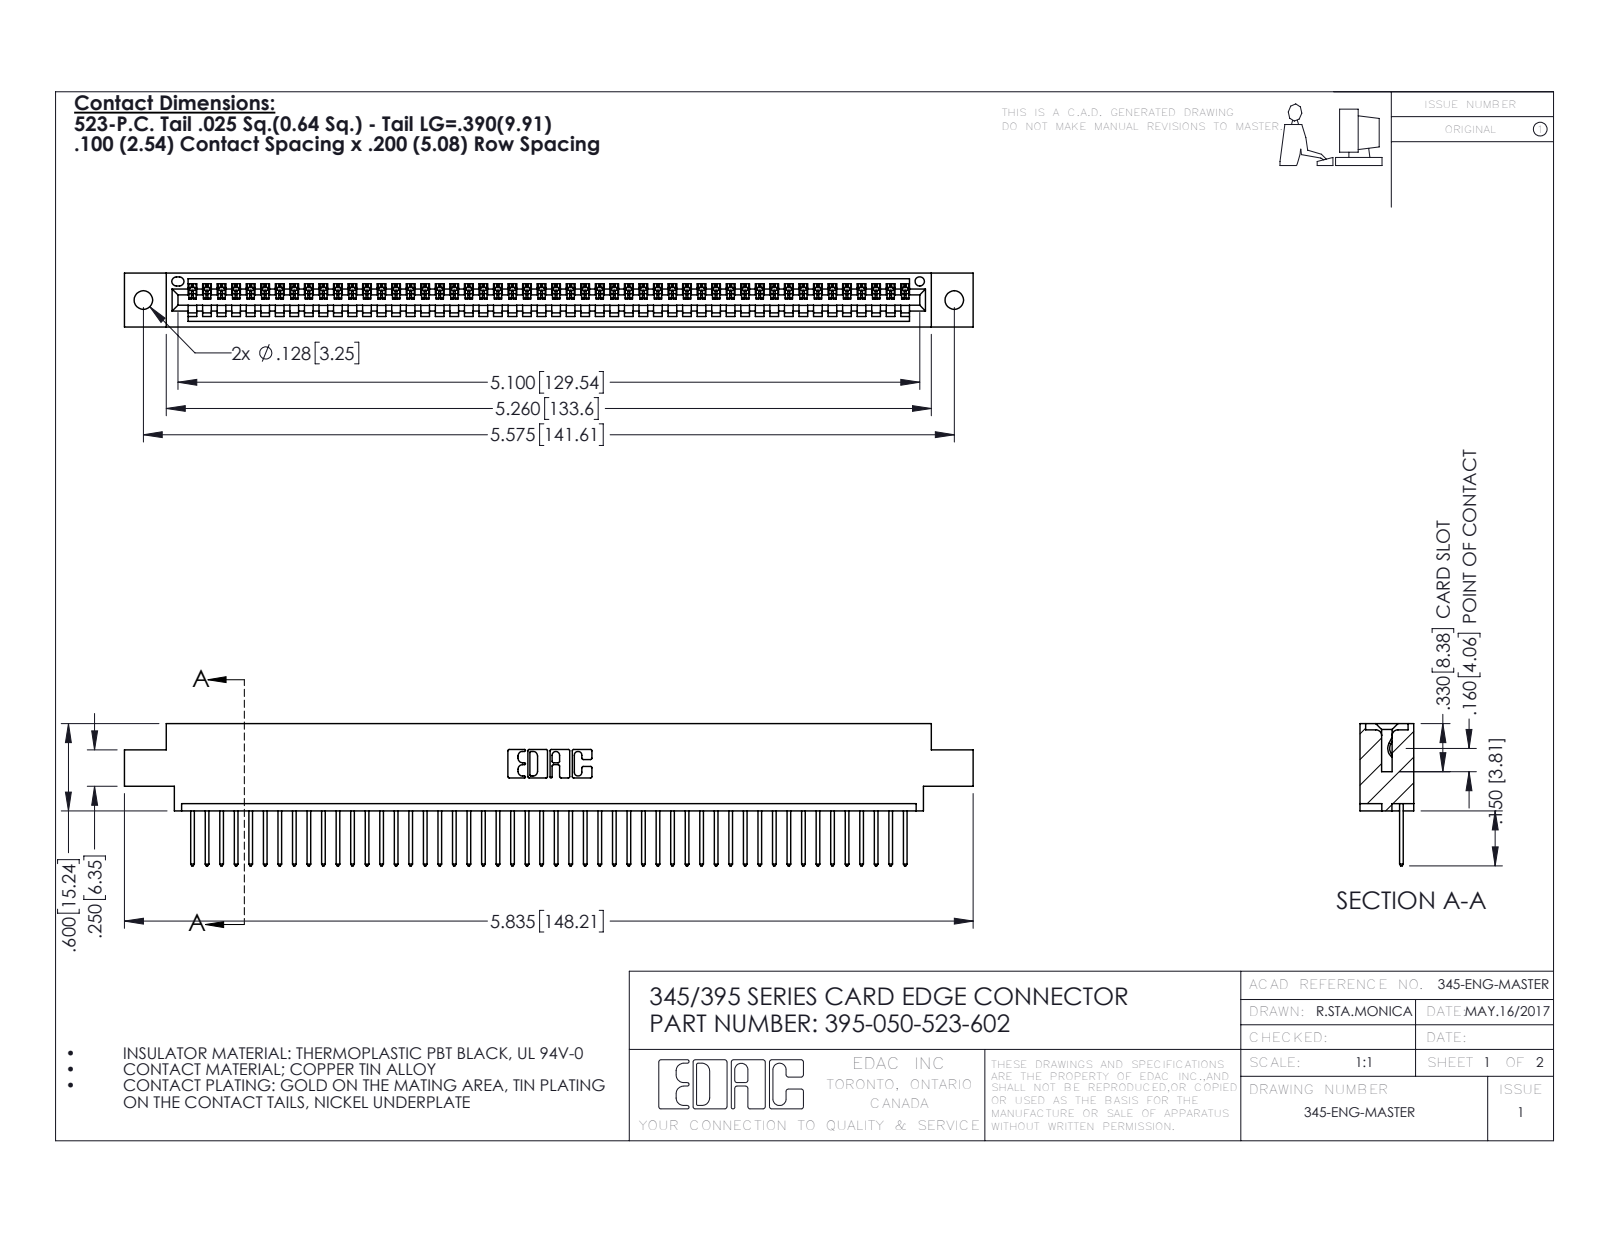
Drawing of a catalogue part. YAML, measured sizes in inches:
part_name: "345 Part_0.170 Offset - 0.128 Dia; 395-050-523-602; 345-292-001_345-293-123"
step_written_by: "SolidWorks 2016 (CONFIG_CONTROL_DESIGN)"
units: inches
bodies: {solids: 51, faces: 3030, planar: 2084, cylindrical: 946, other: 0}
overall_size: [5.835, 0.977, 0.37]
volume: 0.853
surface_area: 28.81
round_holes:
  - {diameter: 0.128, count: 2}
  - {diameter: 0.064, count: 1}
partial_cylinders:
  - {radius: 0.006, count: 100}
  - {radius: 0.01, count: 100}
  - {radius: 0.01, count: 22}
  - {radius: 0.007, count: 6}
  - {radius: 0.031, count: 6}
  - {radius: 0.026, count: 3}
  - {radius: 0.031, count: 2}
  - {radius: 0.04, count: 2}
face_to_face_distances: [0.298, 0.072, 0.37, 0.098, 0.272, 0.025, 0.2, 0.225, 0.175, 0.149]
hole_center_spacings: [0.27, 5.339, 5.575]
